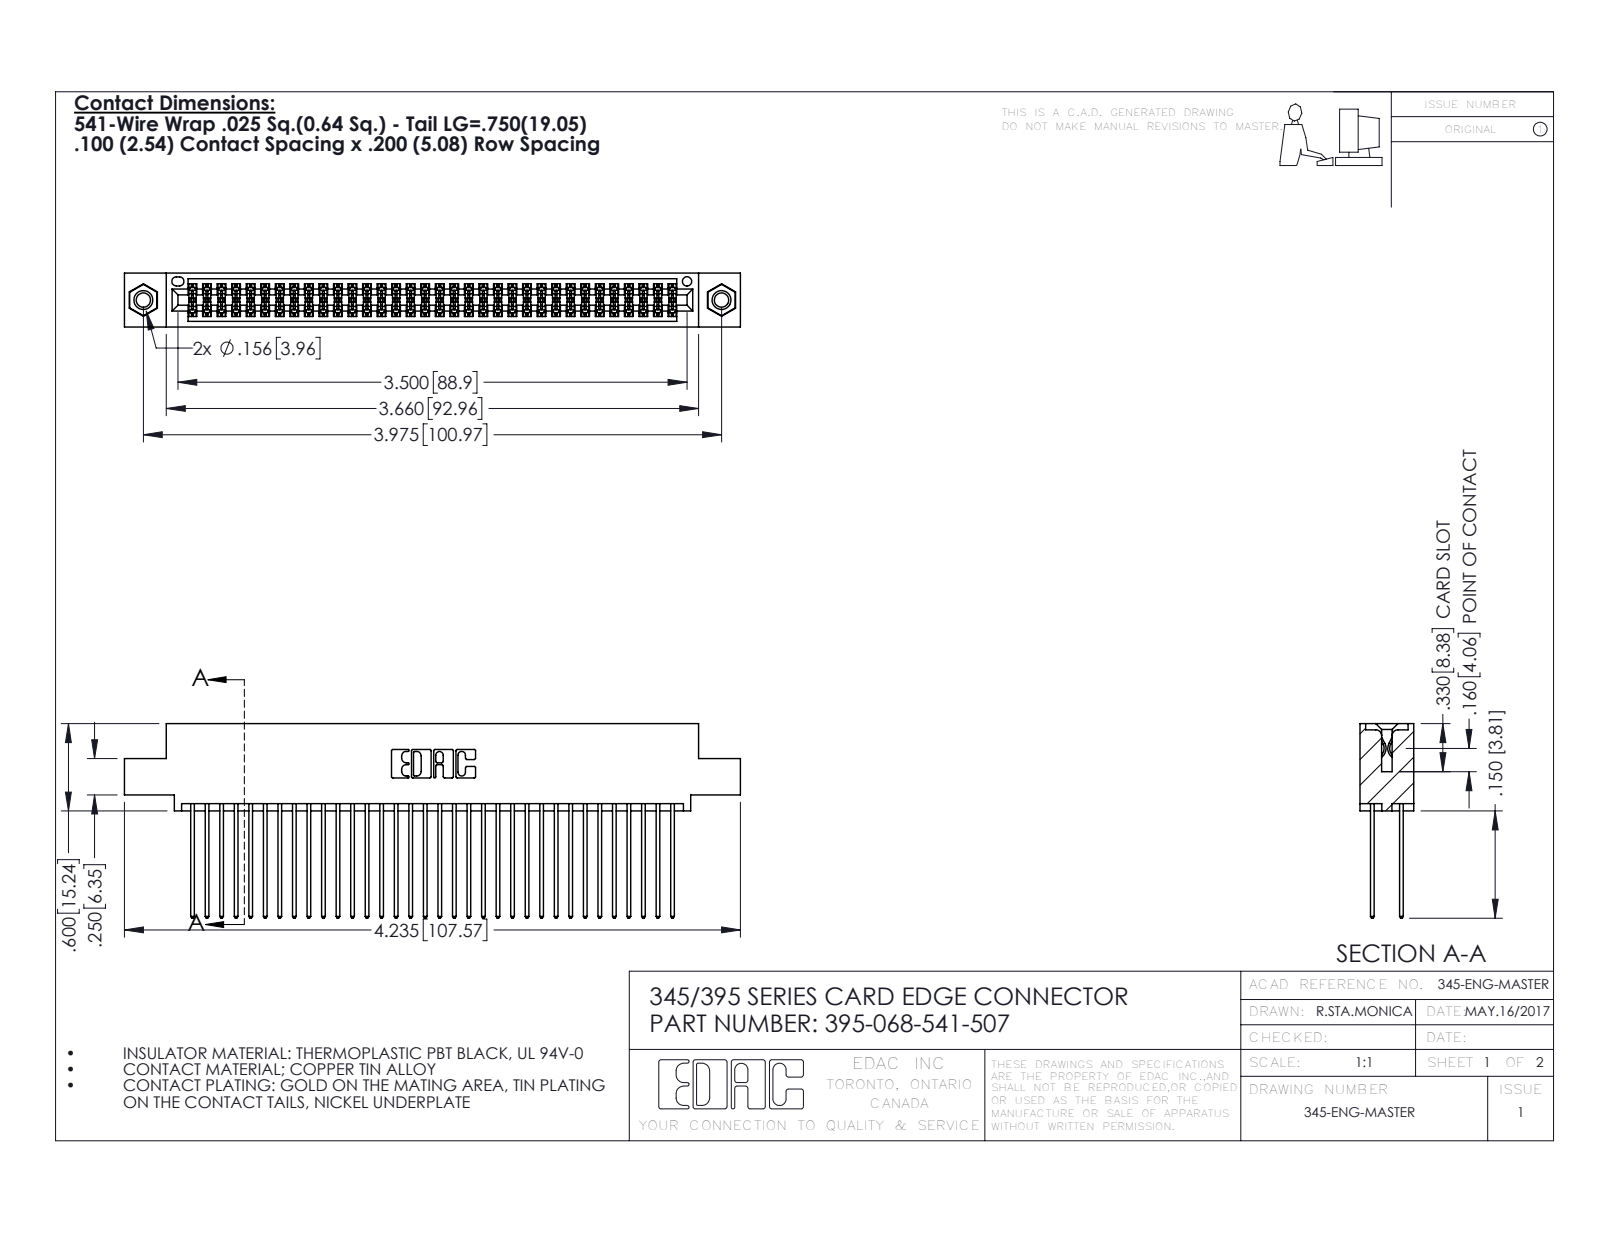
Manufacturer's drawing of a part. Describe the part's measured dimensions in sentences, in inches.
The part is named "345 Part_0.110 Offset - 0.156 Dia-TI; 345-292-001_345-293-141; 345-250-001_345-250-005-103; 395-068-541-507". Its 3-D file was written by "SolidWorks 2016 (CONFIG_CONTROL_DESIGN)". It is 71 solids with 3590 faces: 2360 planar, 1214 cylindrical and 16 other. Overall it measures 4.235 by 1.337 by 0.37 inches. Its volume is 0.652 cubic inches and its surface area 27.26 square inches. Round holes: 2 of diameter 0.098, 2 of diameter 0.125, 2 of diameter 0.156, 1 of diameter 0.064. Round bosses or shafts: 2 of diameter 0.155. Partial cylindrical surfaces (rounded edges, fillets, slot ends): 102 of radius 0.006, 68 of radius 0.01, 22 of radius 0.01, 6 of radius 0.007, 6 of radius 0.031, 3 of radius 0.026, 2 of radius 0.014, 2 of radius 0.019. The main face-to-face distances are 0.072, 0.298, 0.2, 0.098, 0.272, 0.025, 0.225, 0.37, 0.175, 0.149. The hole center spacings are 0.27, 3.74, 3.975.
